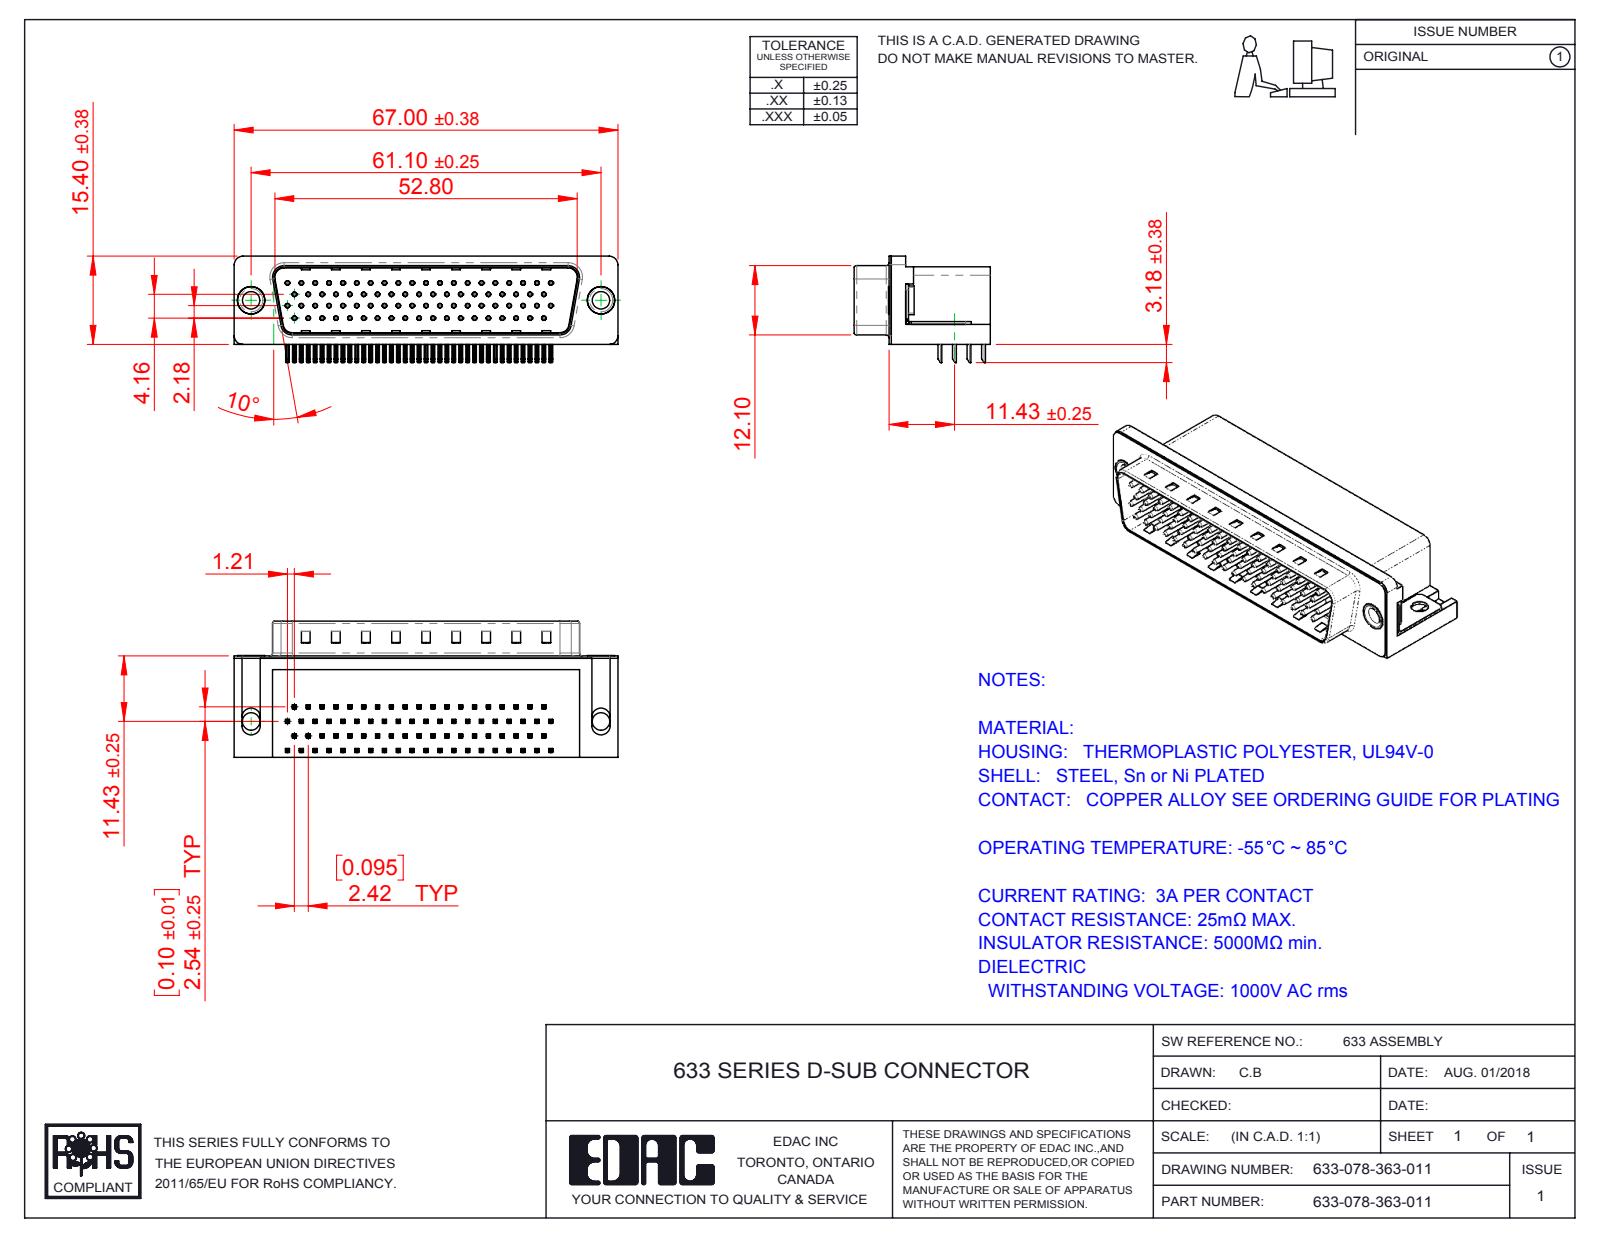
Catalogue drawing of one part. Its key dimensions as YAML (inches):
part_name: "633 Housing_78 Contact; 633 Shell_78 Contact; 633 Thru Hole Rivet; 633 Thru Hole Board Mount_78 Contact (+5 more)"
step_written_by: "SolidWorks 2016 (CONFIG_CONTROL_DESIGN)"
units: inches
bodies: {solids: 84, faces: 6234, planar: 3979, cylindrical: 1760, other: 495}
overall_size: [2.638, 0.937, 0.731]
volume: 0.891
surface_area: 25.29
round_holes:
  - {diameter: 0.014, count: 78}
  - {diameter: 0.031, count: 78}
  - {diameter: 0.12, count: 4}
  - {diameter: 0.157, count: 2}
  - {diameter: 0.189, count: 2}
  - {diameter: 0.197, count: 2}
round_bosses_or_shafts:
  - {diameter: 0.03, count: 78}
  - {diameter: 0.193, count: 2}
  - {diameter: 0.187, count: 2}
  - {diameter: 0.152, count: 2}
partial_cylinders:
  - {radius: 0.01, count: 320}
  - {radius: 0.005, count: 156}
  - {radius: 0.039, count: 16}
  - {radius: 0.02, count: 9}
  - {radius: 0.063, count: 8}
  - {radius: 0.059, count: 6}
  - {radius: 0.018, count: 4}
  - {radius: 0.035, count: 4}
face_to_face_distances: [0.016, 0.52, 0.681, 0.461, 0.526, 0.081, 0.541, 0.065, 0.073, 0.469]
hole_center_spacings: [0.095, 0.191, 0.286, 0.381, 0.246, 0.281, 0.476, 0.339]
